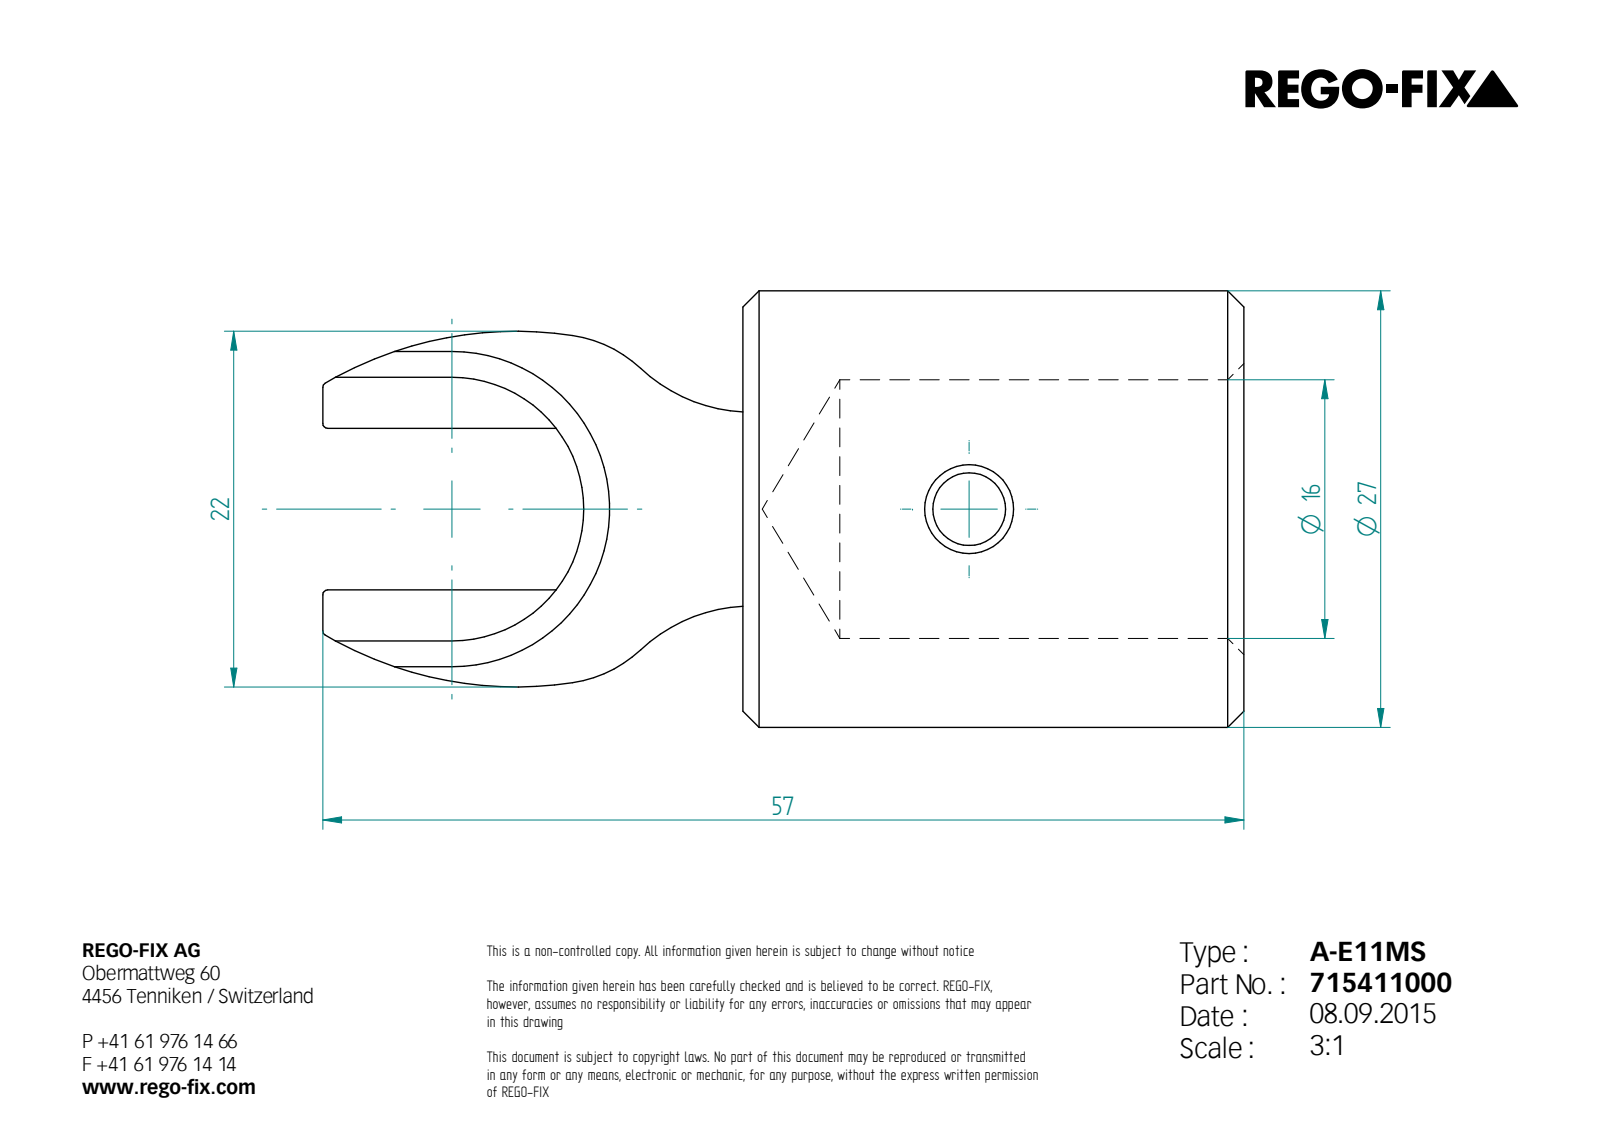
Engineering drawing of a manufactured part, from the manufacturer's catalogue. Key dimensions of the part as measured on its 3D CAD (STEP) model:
STEP written by: Unknown (AUTOMOTIVE_DESIGN)
Units: millimetres
Bodies: 1 solid, 39 faces (16 planar, 16 cylindrical, 7 other)
Overall size (bounding box): 57 × 27 × 27
Volume: 13 004 mm³ · Surface area: 5 945 mm²
Round holes (diameter × count): ⌀4.5 ×1, ⌀5.5 ×1, ⌀16 ×1
Round bosses / shafts (diameter × count): ⌀27 ×1
Partial cylindrical surfaces — rounded edges, fillets, slot ends (radius × count): R0.3 ×4, R7.85 ×2, R10 ×2, R23.5 ×2, R8.15 ×1
Main face-to-face distances: 31, 4, 1.6, 2.4, 0.8, 10.96, 10, 26, 57
